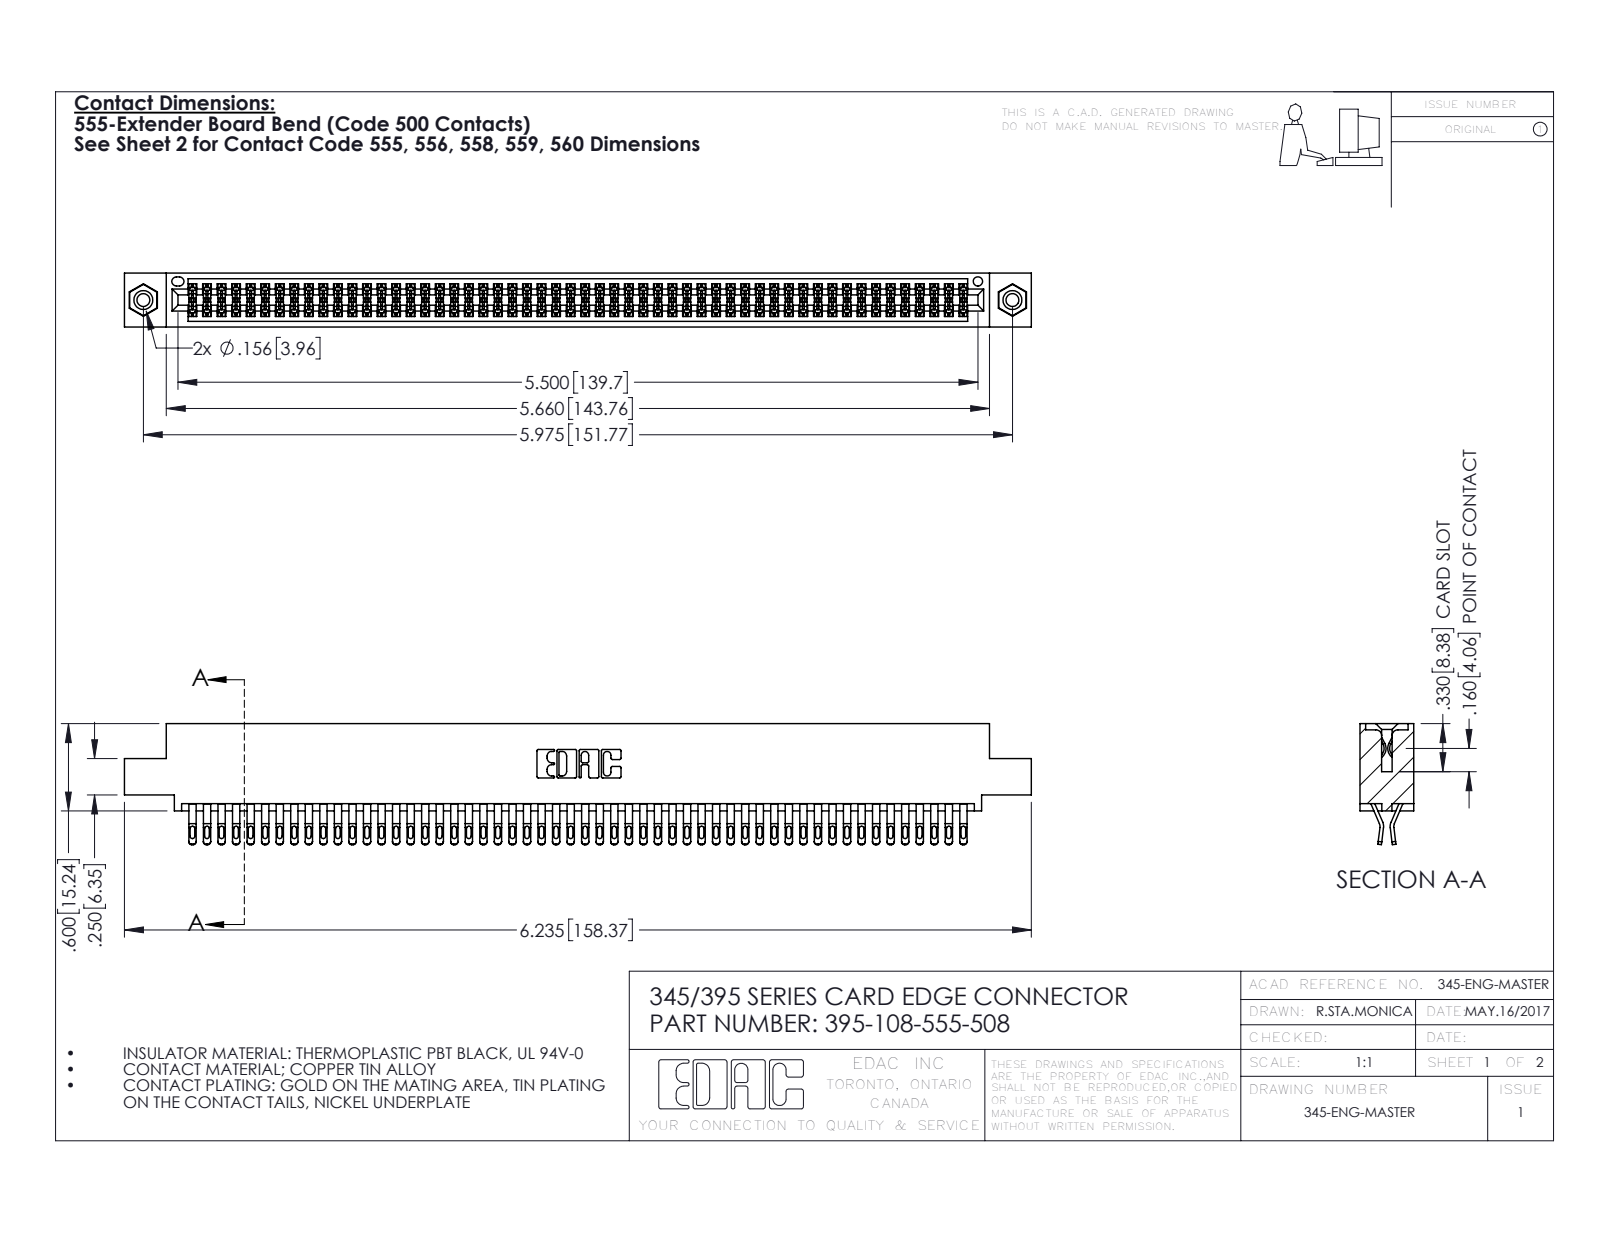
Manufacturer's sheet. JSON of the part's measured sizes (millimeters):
{"part_name": "345-250-001_345-250-003-102; 345-292-001_555 Tail; 395-108-555-508; 345 Part_0.110 Offset - 0.156 Dia-TI", "step_written_by": "SolidWorks 2016 (CONFIG_CONTROL_DESIGN)", "units": "millimeters", "bodies": {"solids": 111, "faces": 6238, "planar": 3464, "cylindrical": 2758, "other": 16}, "overall_size": [158.4, 21.1, 9.4], "volume_mm3": 15700, "surface_area_mm2": 24680, "round_holes": [[2.3, 2], [3.2, 2], [4, 2], [1.6, 1]], "round_bosses_or_shafts": [[3.9, 2]], "partial_cylinders_radius": [[0.4, 270], [0.5, 216], [0.2, 162], [0.3, 22], [0.2, 6], [0.8, 6], [0.7, 3], [0.3, 2]], "face_to_face_distances": [1.8, 7.6, 0.6, 9.4, 5.1, 2.5, 6.9, 5.7, 4.4, 3.8], "hole_center_spacings": [6.9, 145.8, 151.8]}
